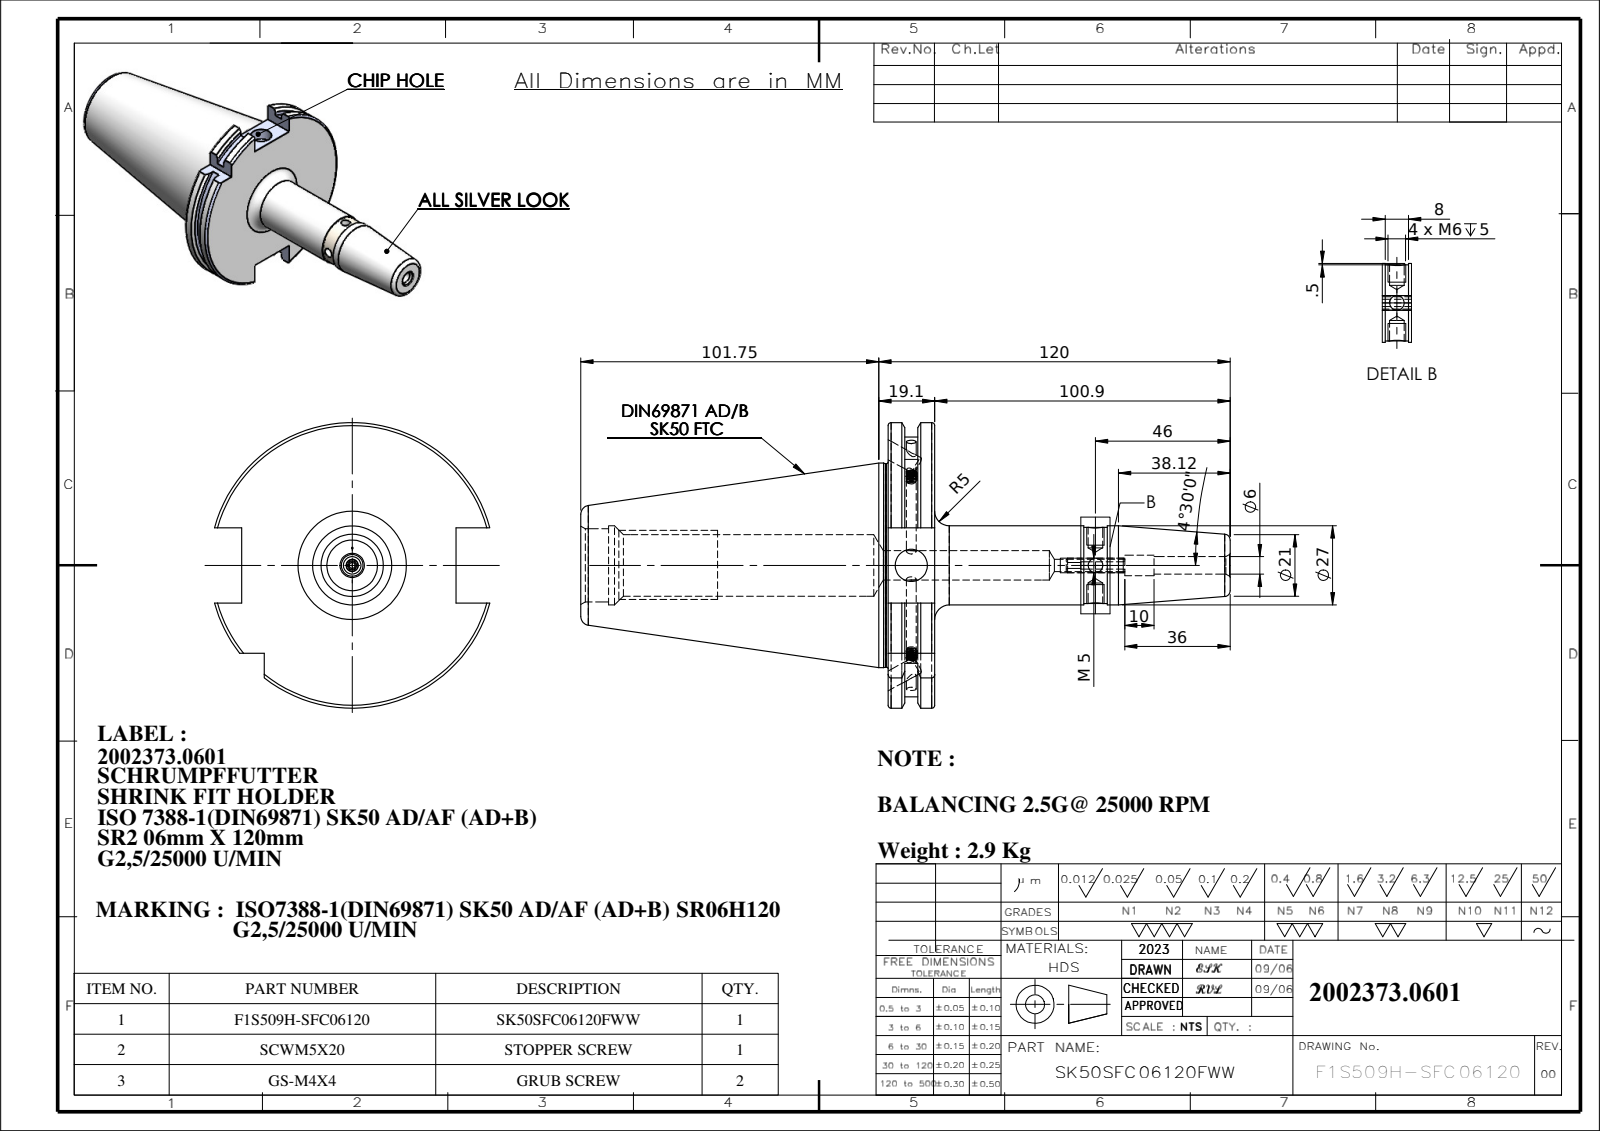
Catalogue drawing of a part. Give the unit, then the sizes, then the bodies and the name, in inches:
Units: inches
Overall size (bounding box): 8.73 × 3.839 × 3.703
Round holes (diameter × count): ⌀0.197 ×2, ⌀0.236 ×2, ⌀0.079 ×1, ⌀0.13 ×1, ⌀0.165 ×1, ⌀0.236 ×1, ⌀0.275 ×1, ⌀0.394 ×1, ⌀0.433 ×1, ⌀0.827 ×1, ⌀0.984 ×1
Round bosses / shafts (diameter × count): ⌀0.157 ×2, ⌀2.75 ×1, ⌀2.734 ×1, ⌀1.063 ×1, ⌀1.024 ×1, ⌀0.197 ×1
Partial cylindrical surfaces — rounded edges, fillets, slot ends (radius × count): R1.768 ×1, R1.919 ×1
Main face-to-face distances: 0.626, 0.223, 0.403, 0.4, 0.177, 0.226, 4.132, 4.355, 4.531, 4.758
Hole centre spacings: 2.476
Volume: 22.66 in³ · Surface area: 86.94 in²
Bodies: 4 solids, 257 faces (60 planar, 83 cylindrical, 114 other)
Part name (STEP PRODUCT): GS-M4X4_DIN 913 - M4 x 4-N; SCWM5X20; SK50SFC06120FWW; 91506-SR206120
STEP written by: SolidWorks 2018 (CONFIG_CONTROL_DESIGN)
